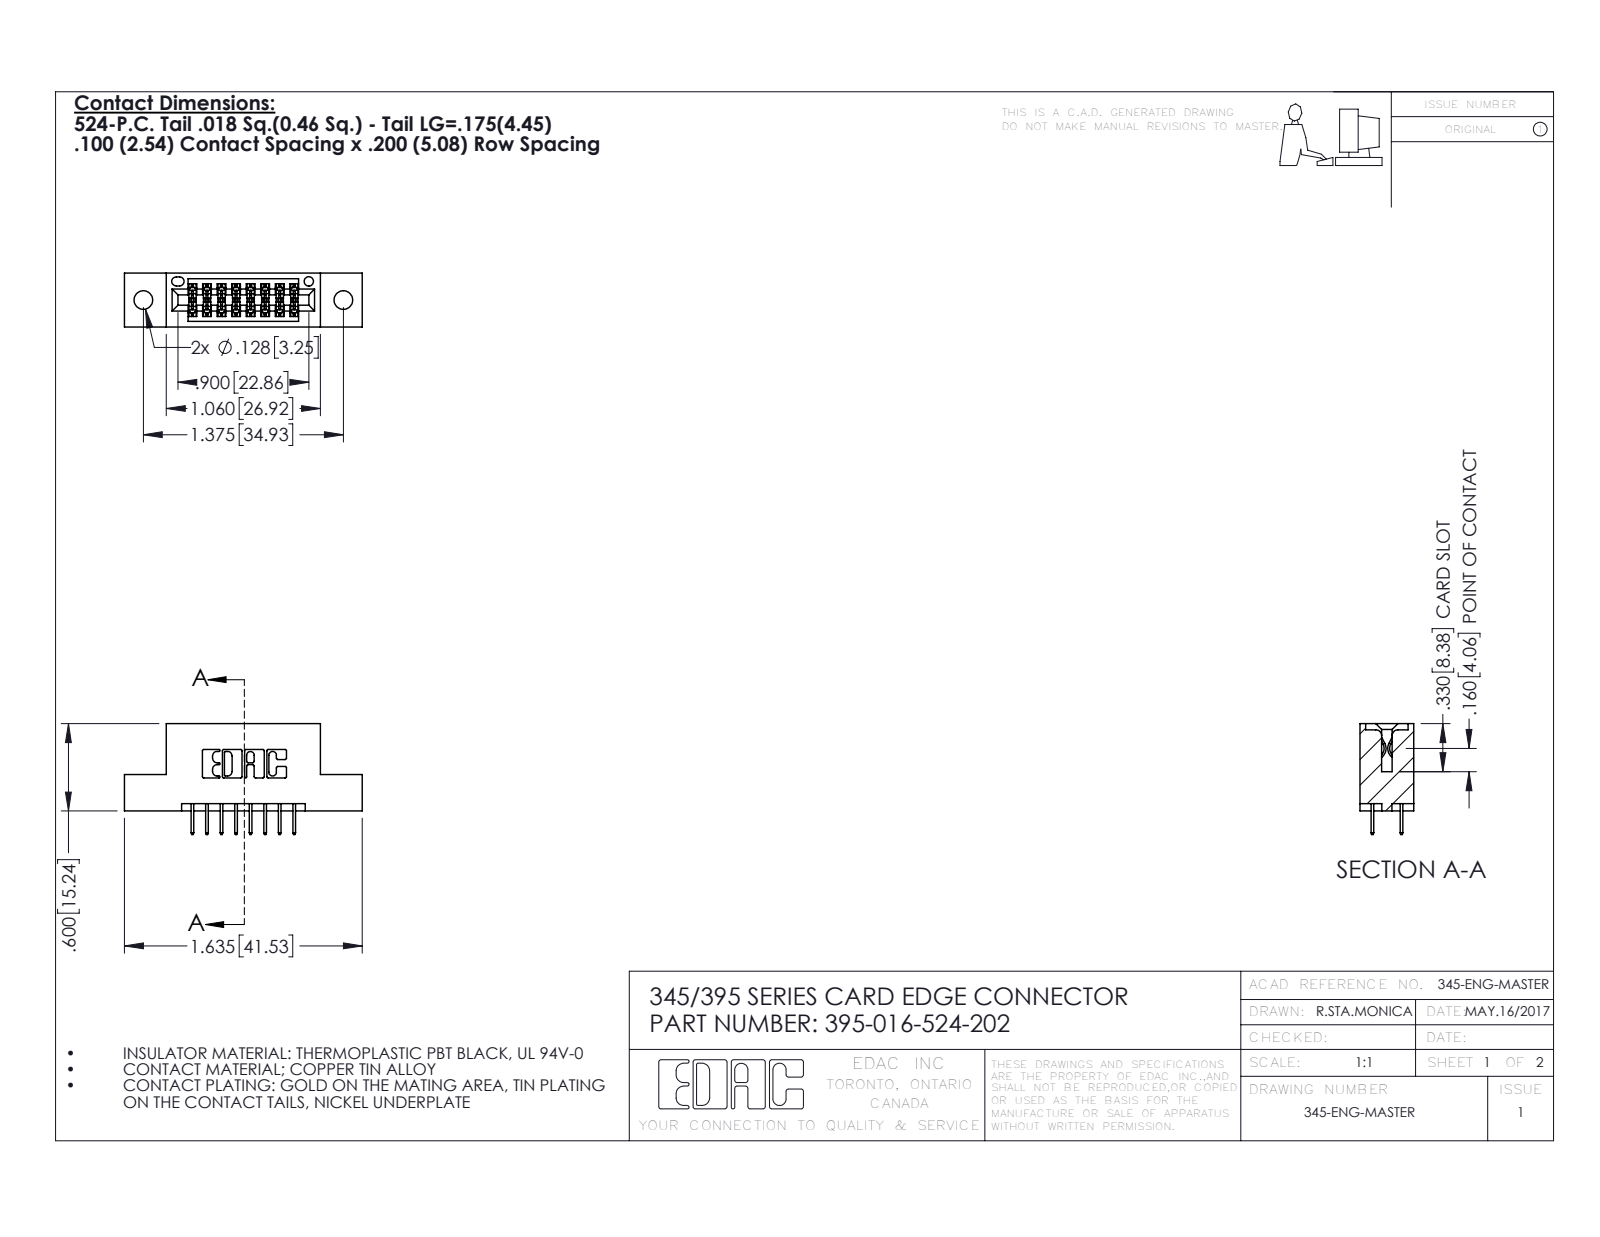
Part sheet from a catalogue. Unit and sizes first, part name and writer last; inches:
Units: inches
Overall size (bounding box): 1.635 × 0.762 × 0.37
Round holes (diameter × count): ⌀0.128 ×2, ⌀0.064 ×1
Partial cylindrical surfaces — rounded edges, fillets, slot ends (radius × count): R0.006 ×24, R0.01 ×22, R0.007 ×6, R0.031 ×6, R0.026 ×3, R0.014 ×2, R0.019 ×2, R0.022 ×2
Main face-to-face distances: 0.2, 0.298, 0.072, 0.37, 0.1, 0.3, 0.098, 0.272, 0.025, 0.06
Hole centre spacings: 0.27, 1.144, 1.375
Volume: 0.223 in³ · Surface area: 6.838 in²
Bodies: 17 solids, 990 faces (704 planar, 286 cylindrical, 0 other)
Part name (STEP PRODUCT): 345-292-001_345-293-124; 345 Part_Flush Mounting Lugs - 0.128 Dia; 395-016-524-202
STEP written by: SolidWorks 2016 (CONFIG_CONTROL_DESIGN)
